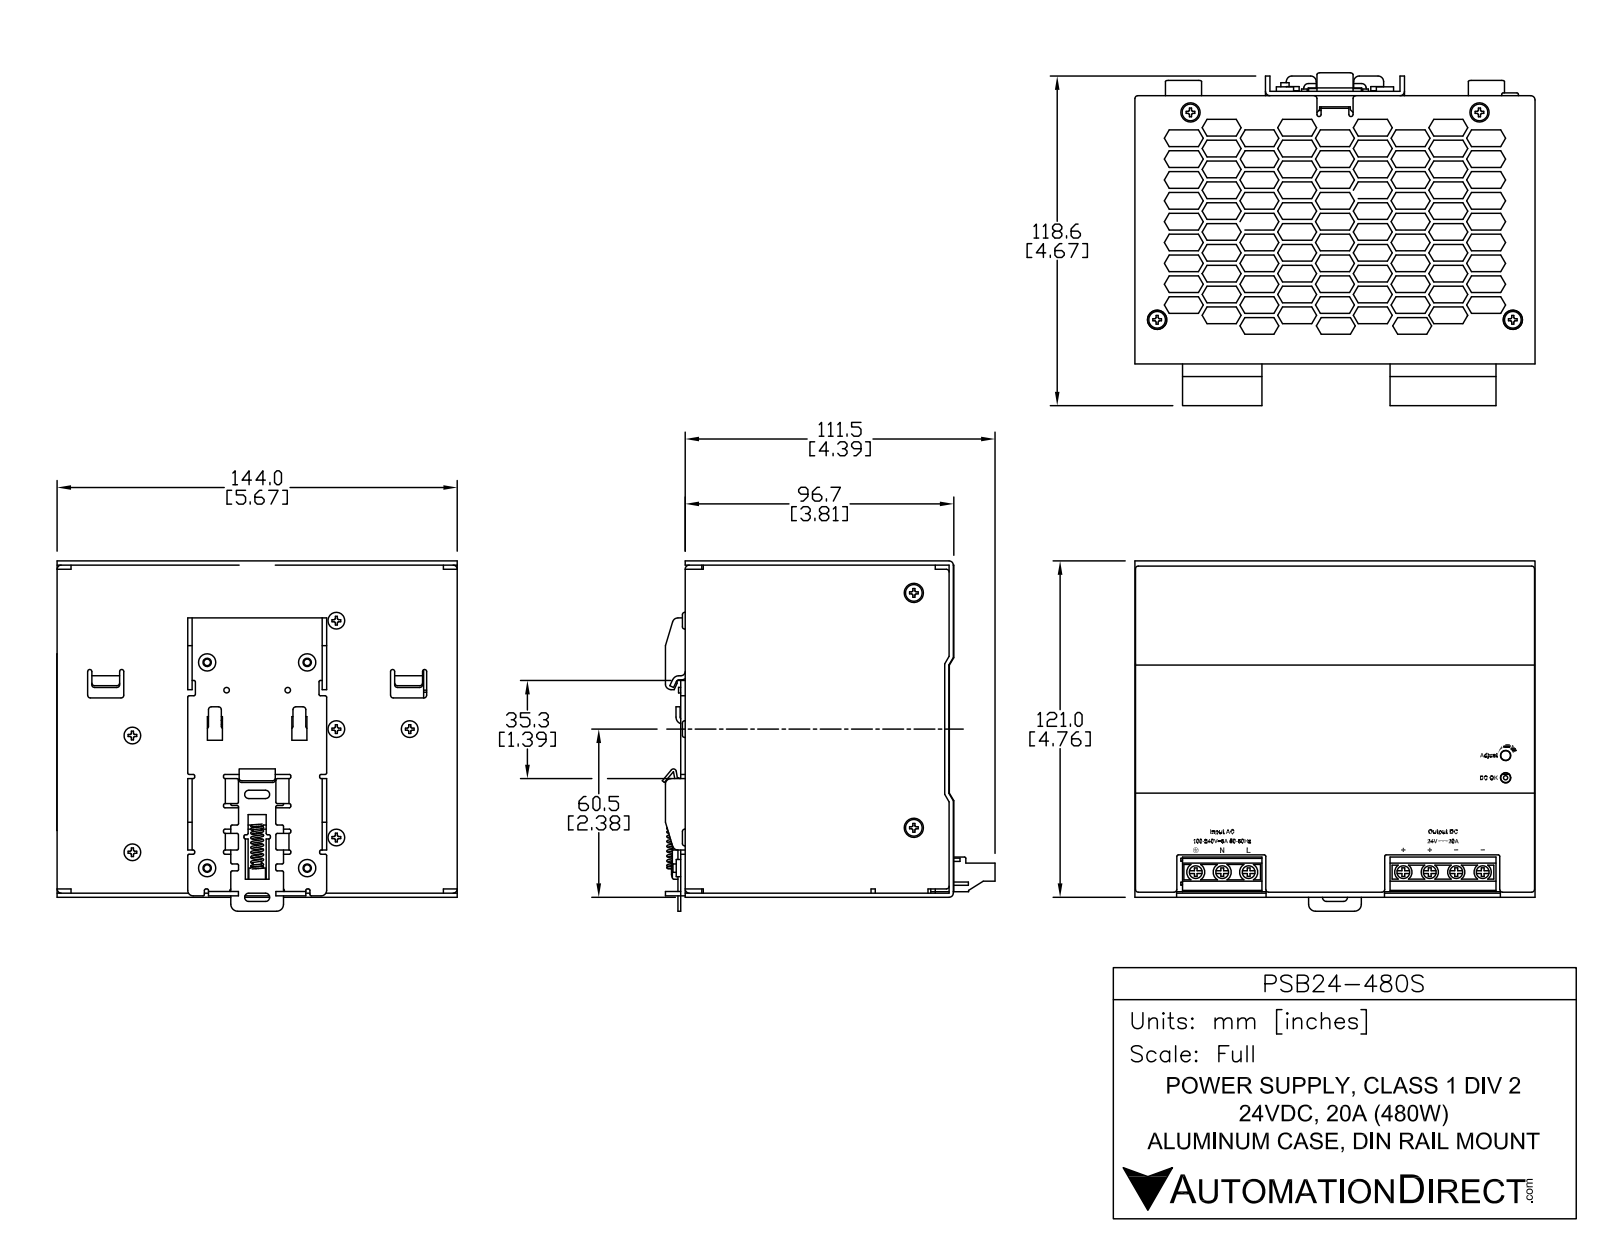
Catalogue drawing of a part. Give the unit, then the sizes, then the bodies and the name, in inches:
Units: inches
Overall size (bounding box): 5.673 × 4.961 × 4.714
Round holes (diameter × count): ⌀0.177 ×13, ⌀0.157 ×10, ⌀0.059 ×7, ⌀0.11 ×7, ⌀0.181 ×7, ⌀0.193 ×7, ⌀0.098 ×6, ⌀0.079 ×5, ⌀0.114 ×5, ⌀0.063 ×4, ⌀0.118 ×4, ⌀0.13 ×4
Round bosses / shafts (diameter × count): ⌀0.236 ×14, ⌀0.118 ×11, ⌀0.126 ×7, ⌀0.079 ×7, ⌀0.244 ×5, ⌀0.232 ×5, ⌀0.138 ×5, ⌀0.184 ×4
Partial cylindrical surfaces — rounded edges, fillets, slot ends (radius × count): R0.02 ×104, R0.039 ×56, R0.03 ×22, R0.059 ×15, R0.079 ×15, R0.063 ×9, R0.01 ×7, R0.035 ×7
Main face-to-face distances: 0.059, 0.063, 3.74, 5.61, 3.543, 0.157, 0.217, 0.28, 5.39, 0.22
Hole centre spacings: 3.316, 2.941, 0.375, 0.376, 3.691, 0.033, 0.75, 0.75
Volume: 11.36 in³ · Surface area: 410.7 in²
Bodies: 55 solids, 4850 faces (3215 planar, 764 cylindrical, 871 other)
Part name (STEP PRODUCT): 0604101305_VR550; 2968123203_DCT-1232; 3461420800_STAND_OFF_M3; 3105472900 (+8 more)
STEP written by: SolidWorks 2014 (AUTOMOTIVE_DESIGN)
